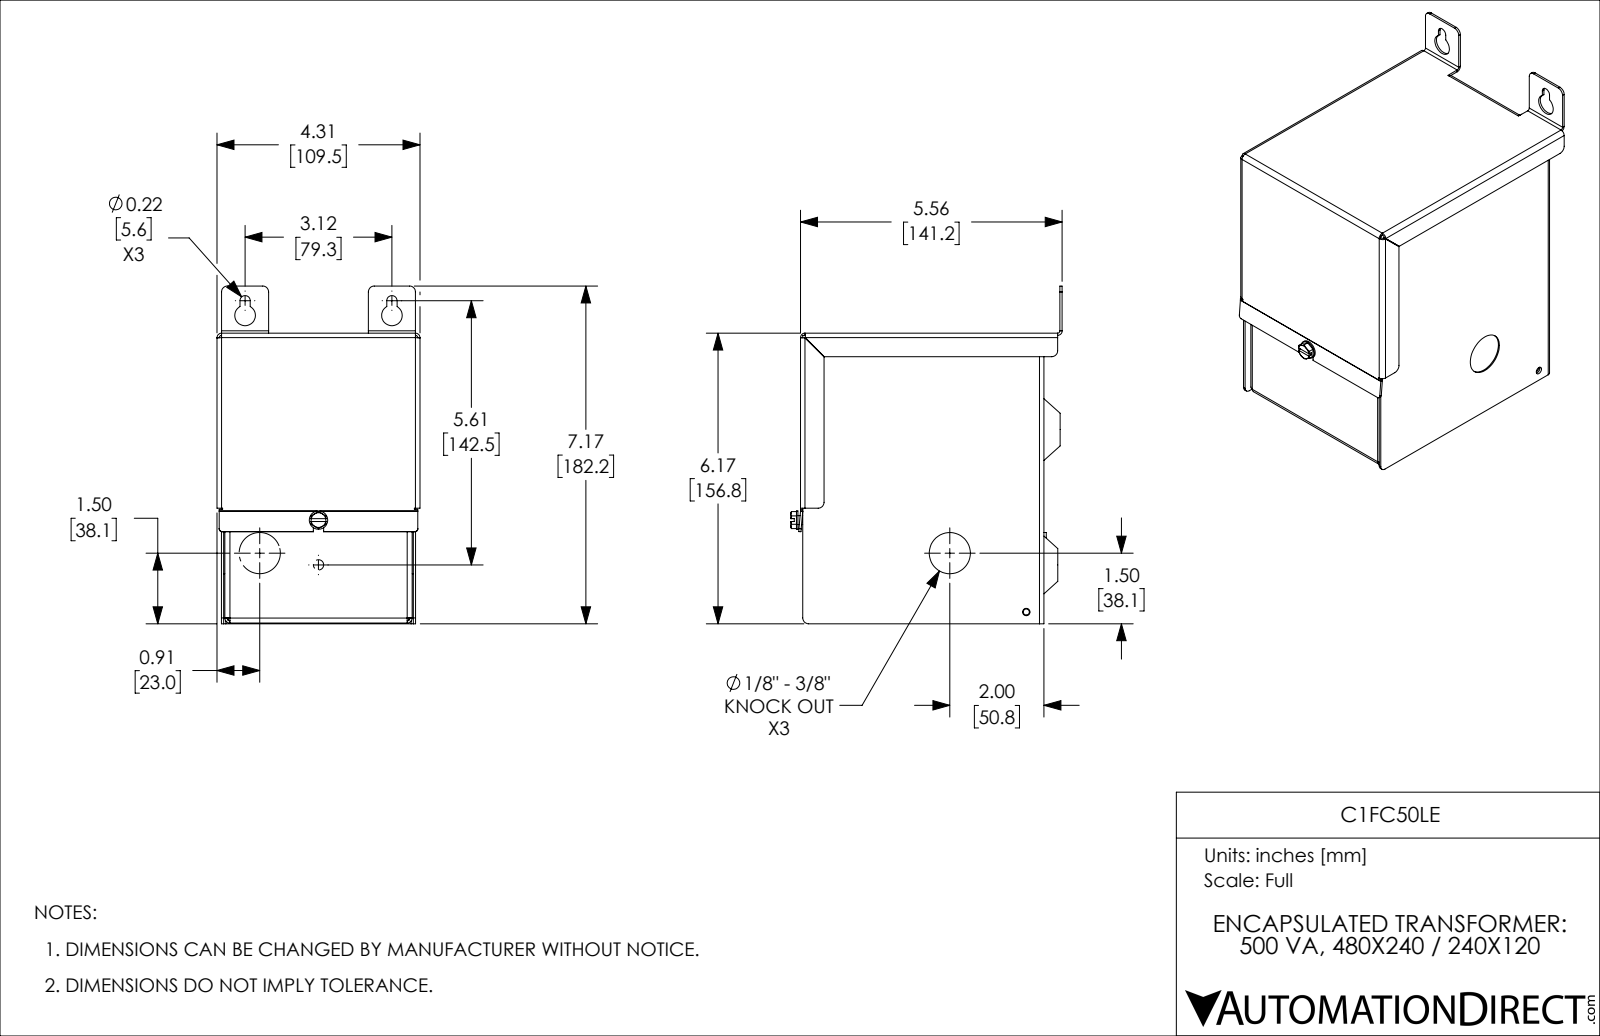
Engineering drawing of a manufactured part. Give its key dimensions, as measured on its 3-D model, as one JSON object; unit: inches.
{"part_name": "NQ1", "step_written_by": "SolidWorks 2017 (AUTOMOTIVE_DESIGN)", "units": "inches", "bodies": {"solids": 4, "faces": 271, "planar": 150, "cylindrical": 91, "other": 30}, "overall_size": [7.173, 5.766, 4.312], "volume_in3": 8.418, "surface_area_in2": 352.6, "round_holes": [[0.157, 2], [0.437, 2], [0.875, 2], [0.13, 1], [0.187, 1], [0.218, 1], [0.281, 1]], "round_bosses_or_shafts": [[0.39, 1], [0.19, 1]], "partial_cylinders_radius": [[0.048, 8], [0.096, 8], [0.125, 8], [0.06, 6], [0.107, 6], [0.048, 2], [0.063, 2], [0.095, 2]], "face_to_face_distances": [0.048, 0.048, 4.077, 6.11, 4.125, 4.029, 6.158, 6.063, 4.993, 5.125], "hole_center_spacings": [2.05, 4.617, 0.952, 1.274, 1.433, 1.46, 1.6, 2.687]}
